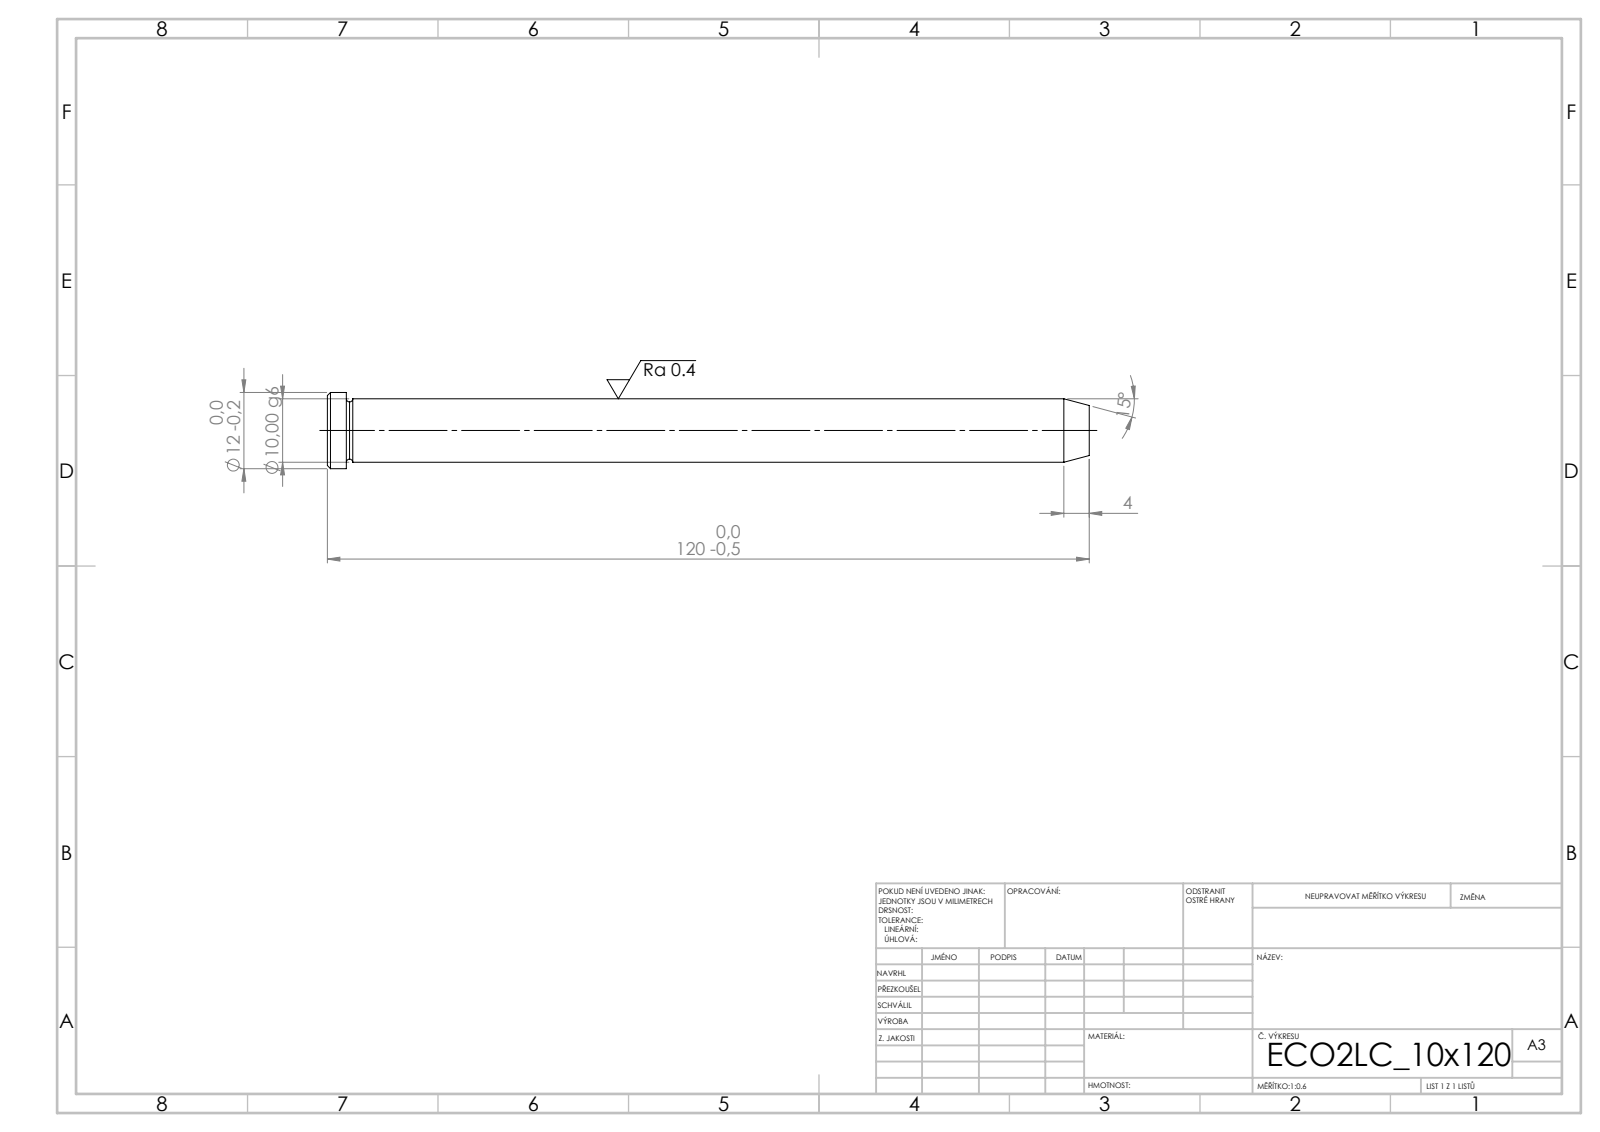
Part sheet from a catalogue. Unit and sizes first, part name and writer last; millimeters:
Units: millimetres
Overall size (bounding box): 120 × 12 × 12
Round bosses / shafts (diameter × count): ⌀12 ×1, ⌀10 ×1
Main face-to-face distances: 120, 117, 3
Volume: 9 450 mm³ · Surface area: 3 979 mm²
Bodies: 1 solid, 15 faces (3 planar, 4 cylindrical, 8 other)
STEP written by: SolidWorks 2019 (CONFIG_CONTROL_DESIGN)
